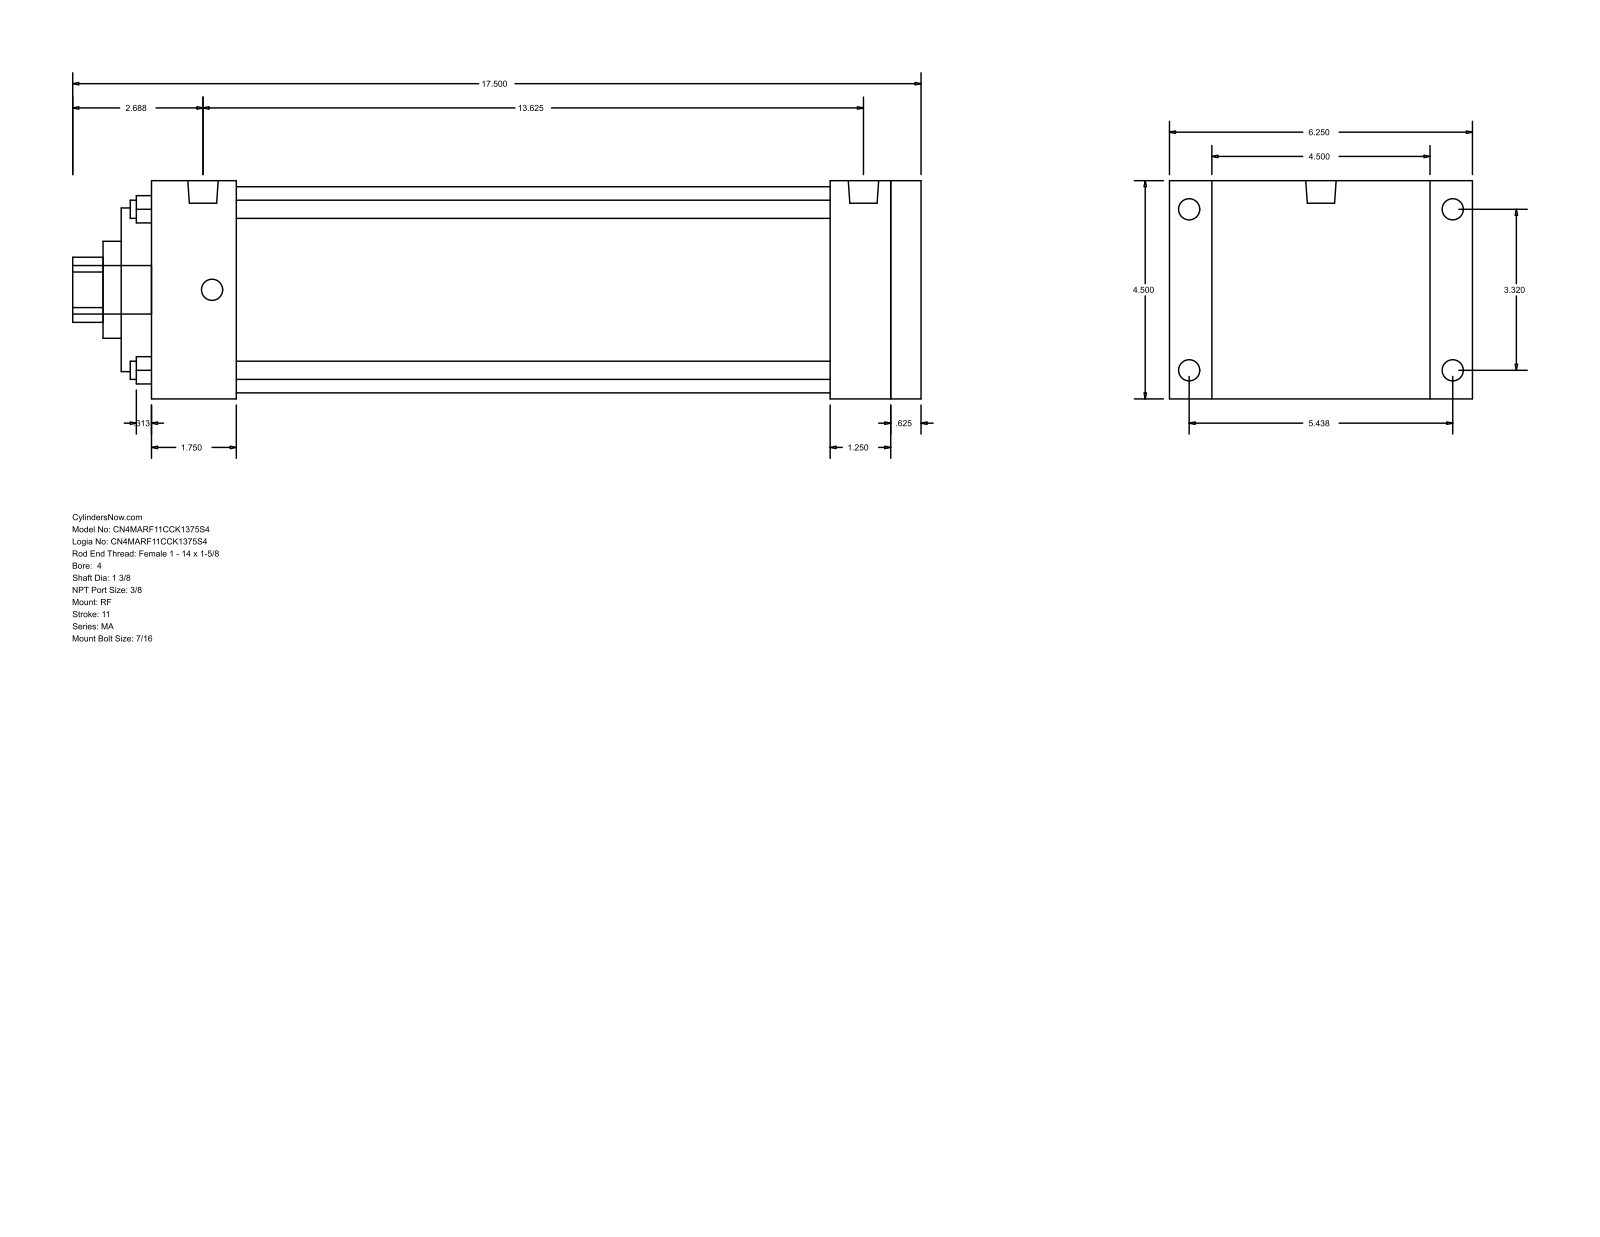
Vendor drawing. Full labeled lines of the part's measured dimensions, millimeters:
Part name (STEP PRODUCT): MA_RF__0400_1.375
STEP written by: GSSL Pune (CONFIG_CONTROL_DESIGN)
Units: millimetres
Bodies: 0 solids, 94 faces (65 planar, 29 cylindrical, 0 other)
Overall size (bounding box): 444.5 × 158.75 × 114.3
Round holes (diameter × count): ⌀9.53 ×4, ⌀34.92 ×1, ⌀50.8 ×1, ⌀85.72 ×1, ⌀107.95 ×1
Round bosses / shafts (diameter × count): ⌀11.11 ×8, ⌀15.93 ×2, ⌀25.4 ×1
Partial cylindrical surfaces — rounded edges, fillets, slot ends (radius × count): R17.06 ×1
Main face-to-face distances: 114.3, 403.23, 15.88, 387.35, 15.87, 403.22, 419.1, 22.23, 136.53, 371.48
Hole centre spacings: 59.62, 84.32, 119.25
